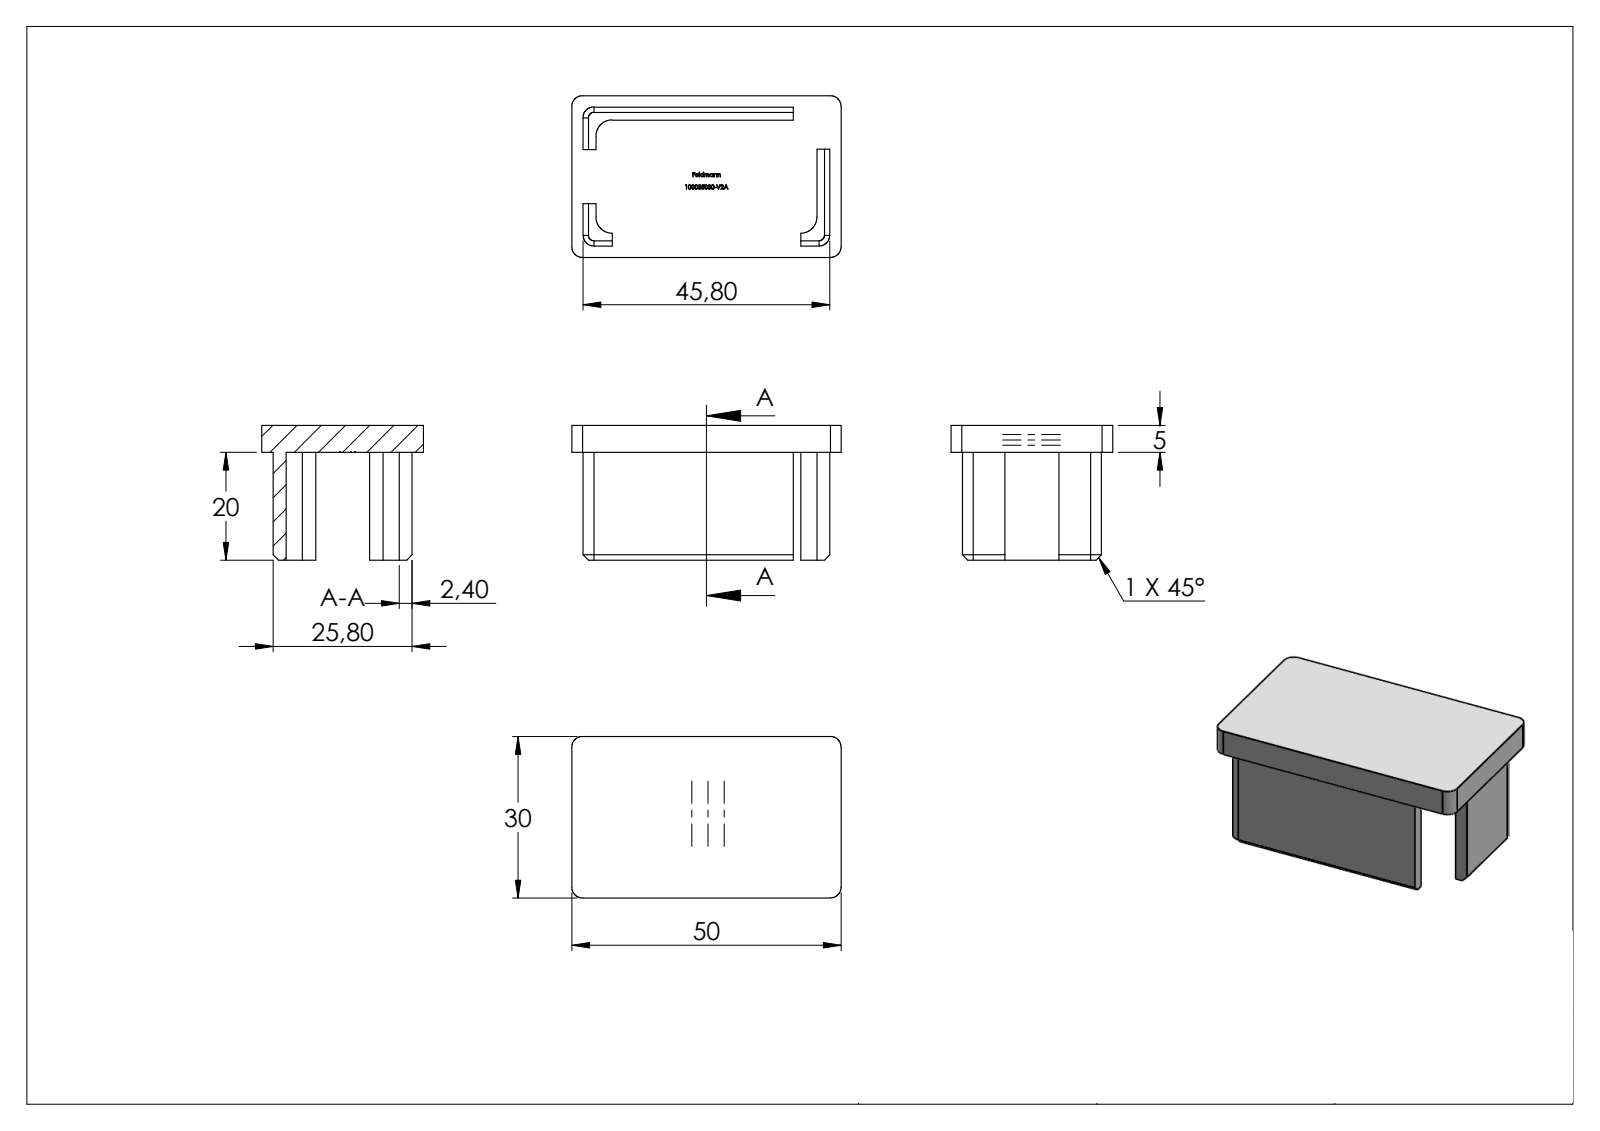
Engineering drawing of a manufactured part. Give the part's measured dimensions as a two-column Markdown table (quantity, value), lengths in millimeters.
| quantity | value |
| --- | --- |
| part name | 100035030-V2A |
| STEP written by | SolidWorks 2015 (CONFIG_CONTROL_DESIGN) |
| units | millimeters |
| bodies | 1 solid, 309 faces (161 planar, 10 cylindrical, 138 other) |
| overall size | 60 × 40 × 25 |
| volume | 17 099 mm³ |
| surface area | 10 129 mm² |
| partial cylindrical surfaces (radius × count) | 2 × 7, 3 × 3 |
| main face-to-face distances | 5, 2.4, 2.1, 53.4, 4.5, 55.8, 37.9, 55.5, 57.9, 51 |
